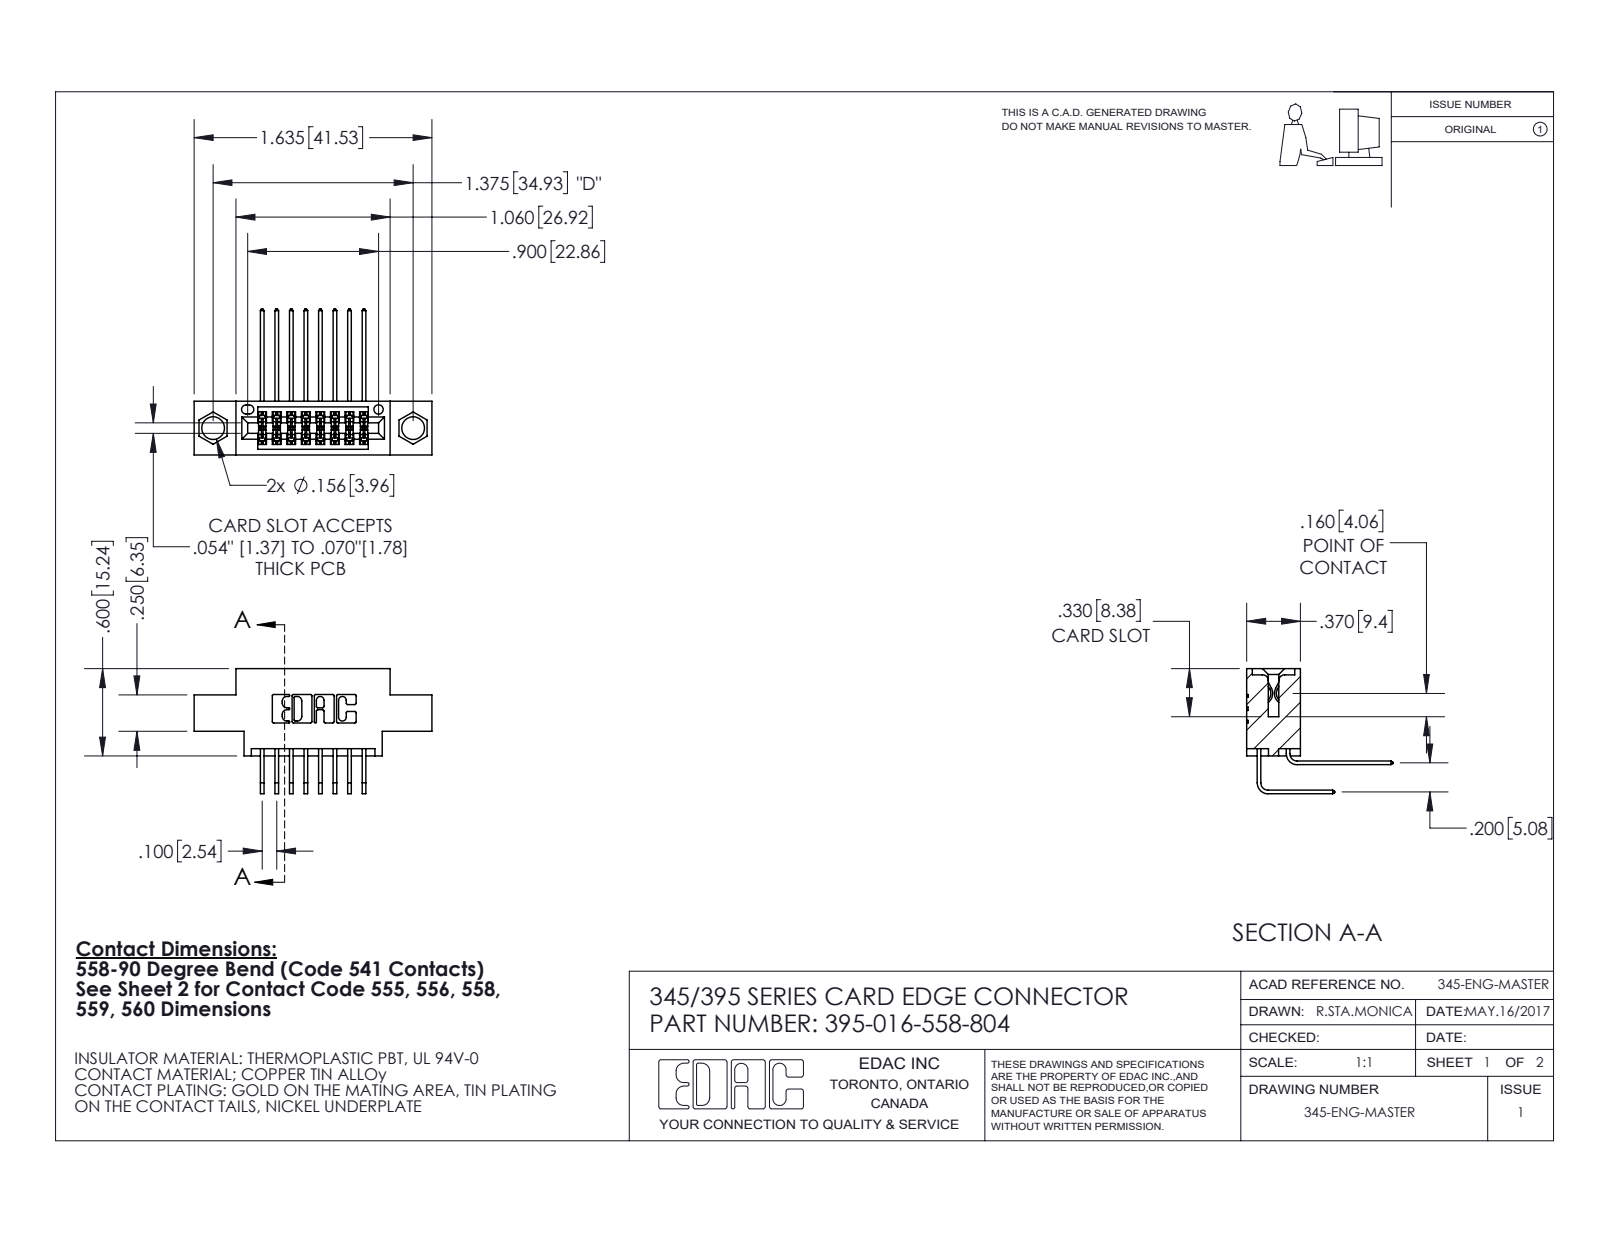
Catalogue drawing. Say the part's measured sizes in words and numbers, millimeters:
The part is named "395-016-558-804; 345-292-001_558 559 Tail - 1; 345 Part_0.170 Offset - 0.156 Dia-TI; 345-292-001_558 Tail - 2". Its 3-D file was written by "SolidWorks 2020 (CONFIG_CONTROL_DESIGN)". It is 17 solids with 976 faces: 658 planar, 318 cylindrical and 0 other. Overall it measures 41.5 by 25.5 by 21.8 millimeters. Its volume is 3 590 cubic millimeters and its surface area 5 079 square millimeters. Round holes: 2 of diameter 4, 1 of diameter 1.6. Partial cylindrical surfaces (rounded edges, fillets, slot ends): 24 of radius 0.2, 22 of radius 0.3, 6 of radius 0.2, 6 of radius 0.8, 3 of radius 0.7, 2 of radius 0.4, 2 of radius 0.5, 2 of radius 0.6. The main face-to-face distances are 5.1, 9.4, 1.8, 7.6, 2.5, 2.5, 6.9, 0.6, 5.7, 1.5. The hole center spacings are 6.9, 29.1, 34.9.
